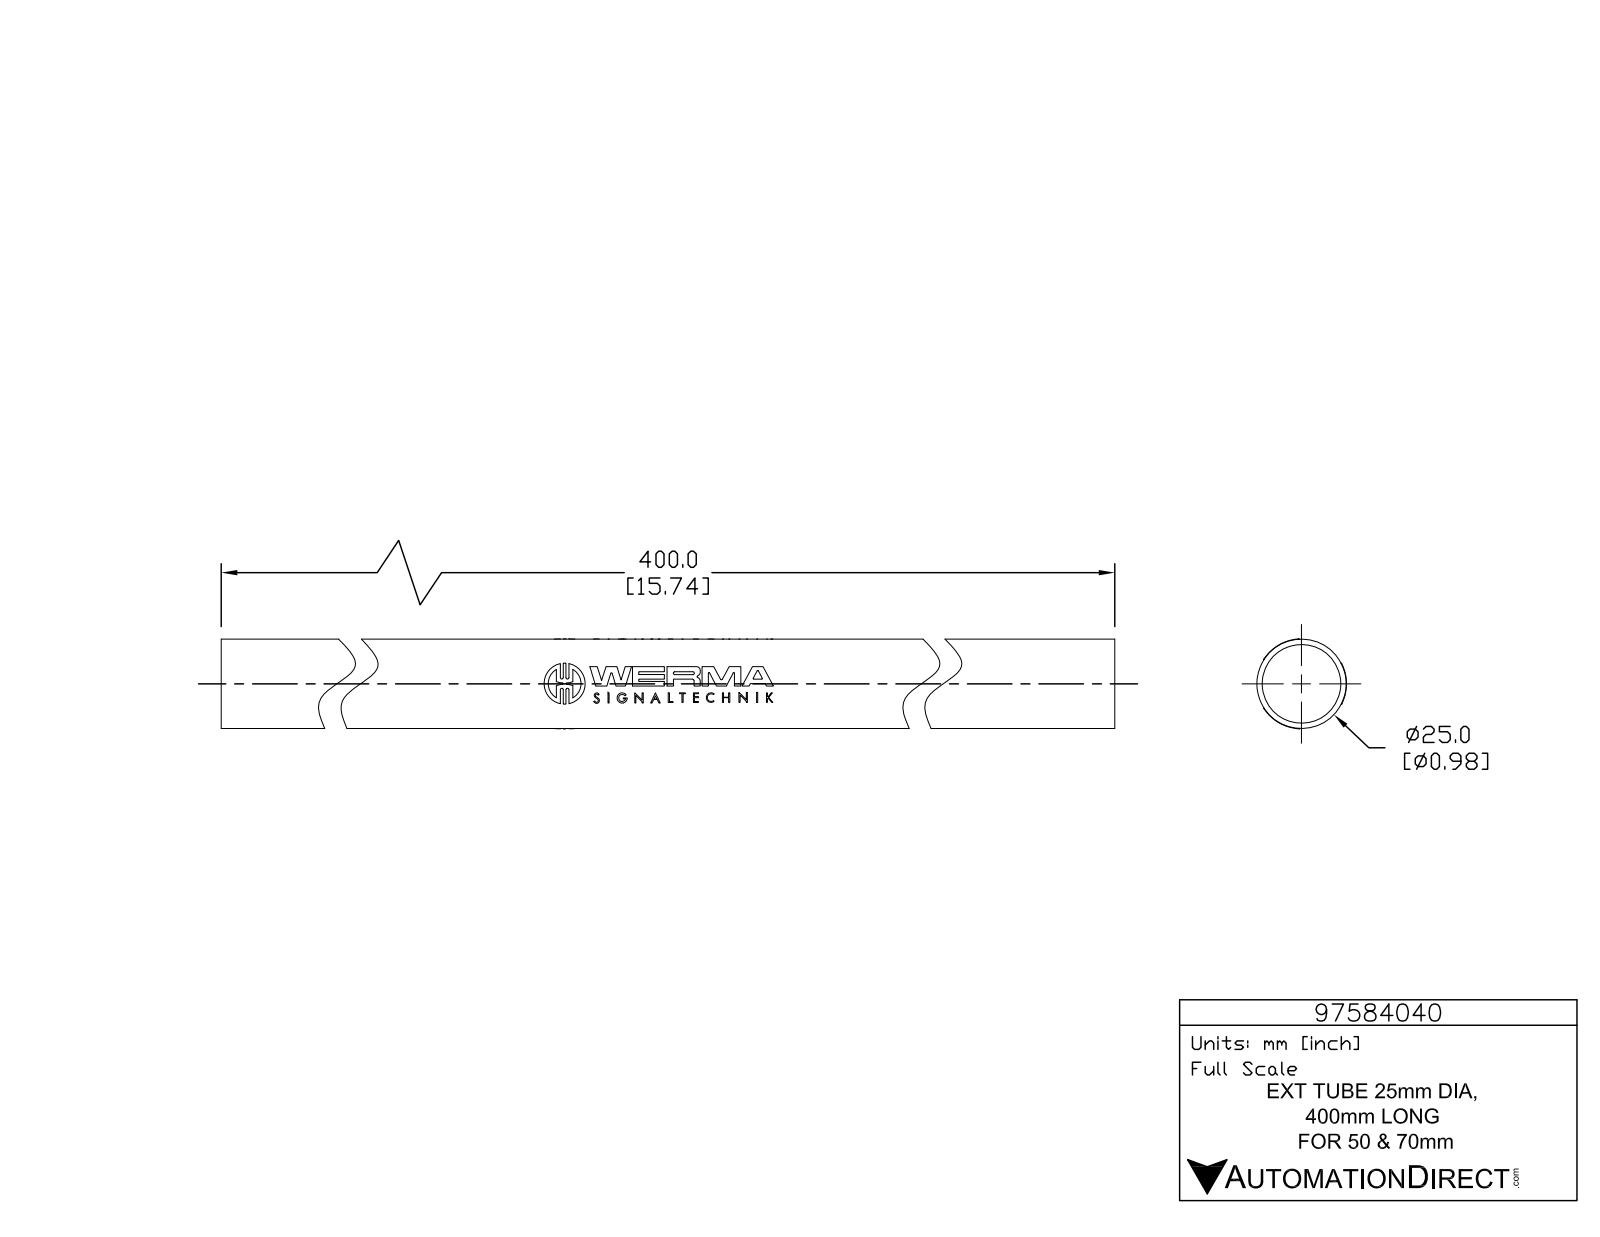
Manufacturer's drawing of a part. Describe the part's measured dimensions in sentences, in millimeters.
The part is named "97584040". Its 3-D file was written by "SolidWorks 2015 (AUTOMOTIVE_DESIGN)". It is 1 solid with 6 faces: 2 planar, 4 cylindrical and 0 other. Overall it measures 399.8 by 24.9 by 24.9 millimeters. Its volume is 80 610 cubic millimeters and its surface area 55 590 square millimeters. Round holes: 1 of diameter 19.1. Round bosses or shafts: 1 of diameter 24.9. The main face-to-face distances are 399.8.
